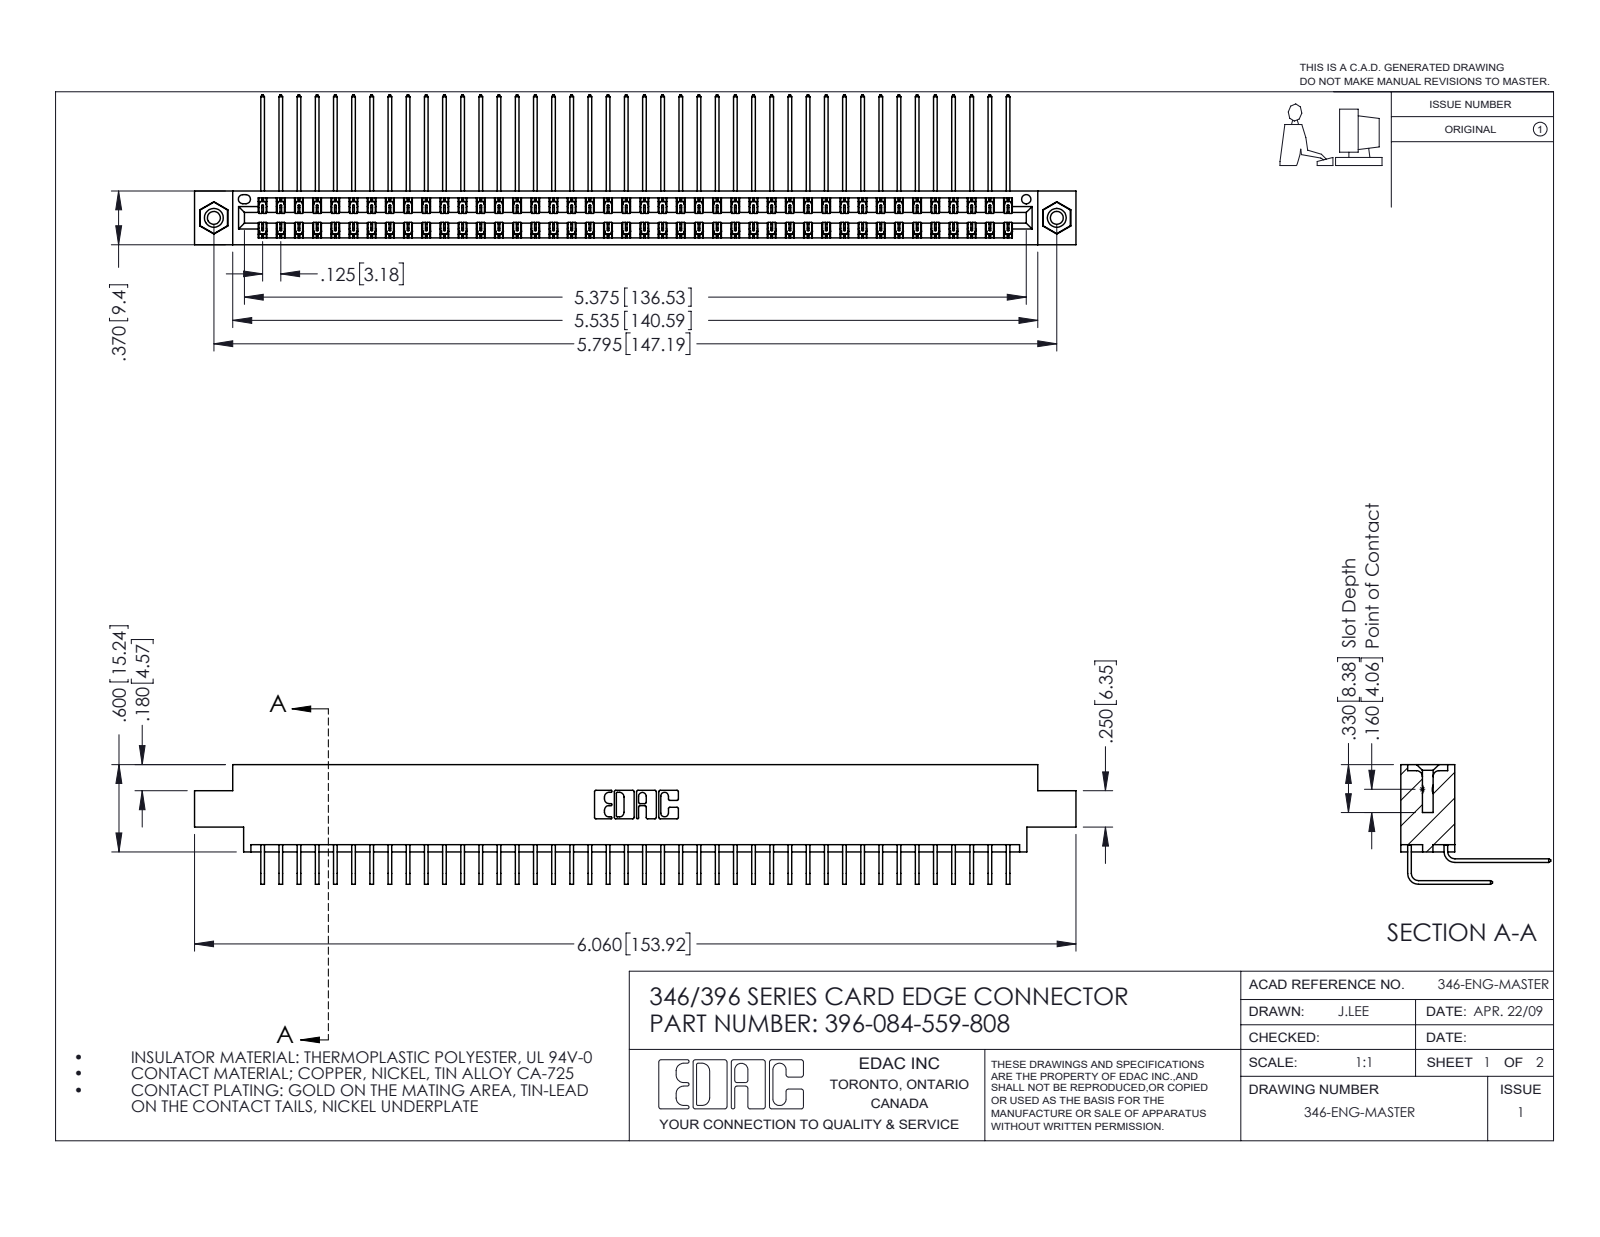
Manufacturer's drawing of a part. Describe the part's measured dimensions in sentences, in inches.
The part is named "345-250-001_345-250-003-102; 396-084-559-808; 345-292-001_559 Tail - 2; 345-292-001_558 559 Tail - 1 (+1 more)". Its 3-D file was written by "SolidWorks 2016 (CONFIG_CONTROL_DESIGN)". It is 87 solids with 4722 faces: 3220 planar, 1486 cylindrical and 16 other. Overall it measures 6.06 by 1.03 by 0.823 inches. Its volume is 0.936 cubic inches and its surface area 36.58 square inches. Round holes: 2 of diameter 0.089, 2 of diameter 0.125, 2 of diameter 0.156, 1 of diameter 0.064. Round bosses or shafts: 2 of diameter 0.155. Partial cylindrical surfaces (rounded edges, fillets, slot ends): 126 of radius 0.006, 22 of radius 0.01, 6 of radius 0.007, 6 of radius 0.031, 3 of radius 0.026, 2 of radius 0.014, 2 of radius 0.022, 2 of radius 0.024. The main face-to-face distances are 0.048, 0.322, 0.025, 0.37, 0.25, 0.072, 0.298, 0.275, 0.222, 0.148. The hole center spacings are 0.246, 5.586, 5.795.
